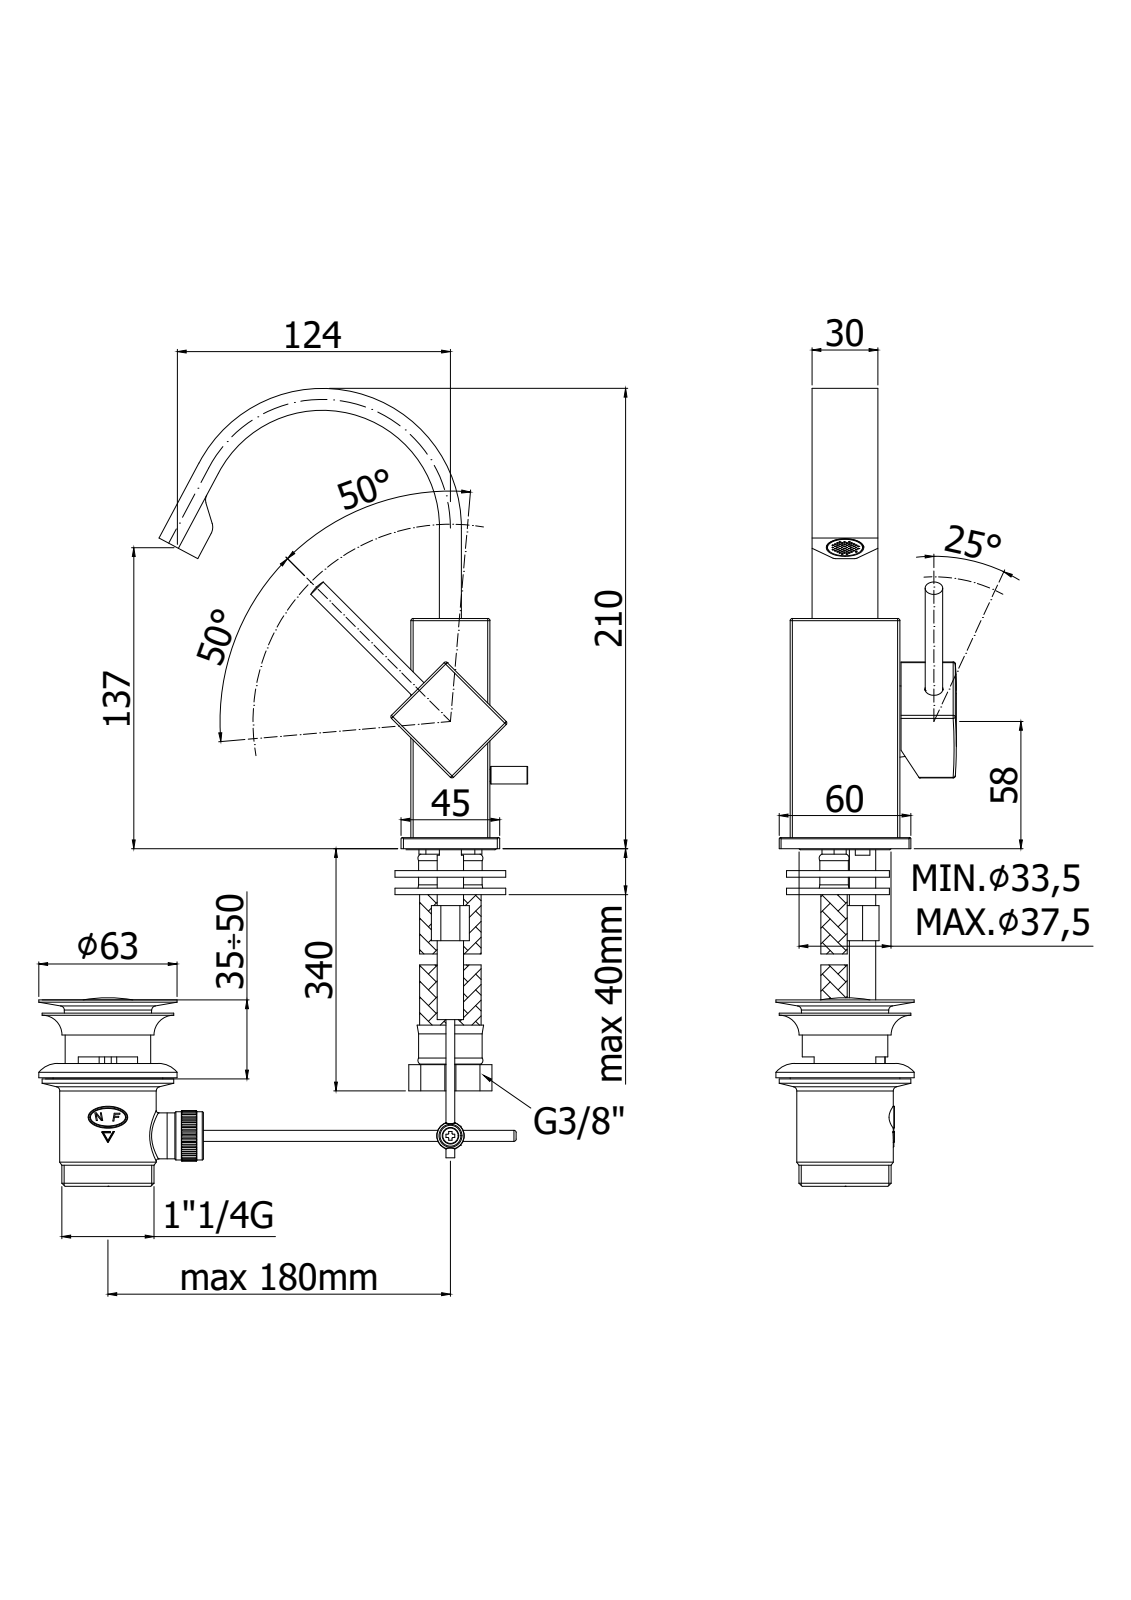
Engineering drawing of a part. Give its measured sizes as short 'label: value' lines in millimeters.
name: LEA837CR
written by: CREO PARAMETRIC BY PTC INC, 2020044 (CONFIG_CONTROL_DESIGN)
unit: mm
bodies: 5 solids, 3238 faces (2031 planar, 706 cylindrical, 501 other)
size: 210 × 160.93 × 82.98
volume: 225 894 mm³; area: 99 678 mm²
holes: 4× ⌀11, 3× ⌀3.3, 3× ⌀4.5, 3× ⌀6, 3× ⌀7, 2× ⌀4.6, 2× ⌀5, 2× ⌀9, 2× ⌀34, 1× ⌀3, 1× ⌀4, 1× ⌀5.5
bosses: 3× ⌀0.9, 2× ⌀20, 2× ⌀12, 2× ⌀10.8, 2× ⌀8.2, 2× ⌀4, 1× ⌀38.8, 1× ⌀32
rounds: 64× R0.5, 51× R0.12, 19× R1, 10× R0.7, 8× R0.6, 6× R0.8, 4× R0.65, 4× R0.85
face distances: 10, 1.5, 36, 40, 13, 8.5, 11.5, 30, 28.5, 38.5
hole spacings: 5.96, 6.72, 9.43, 10.12, 11.2, 11.31, 15.26, 18.07
